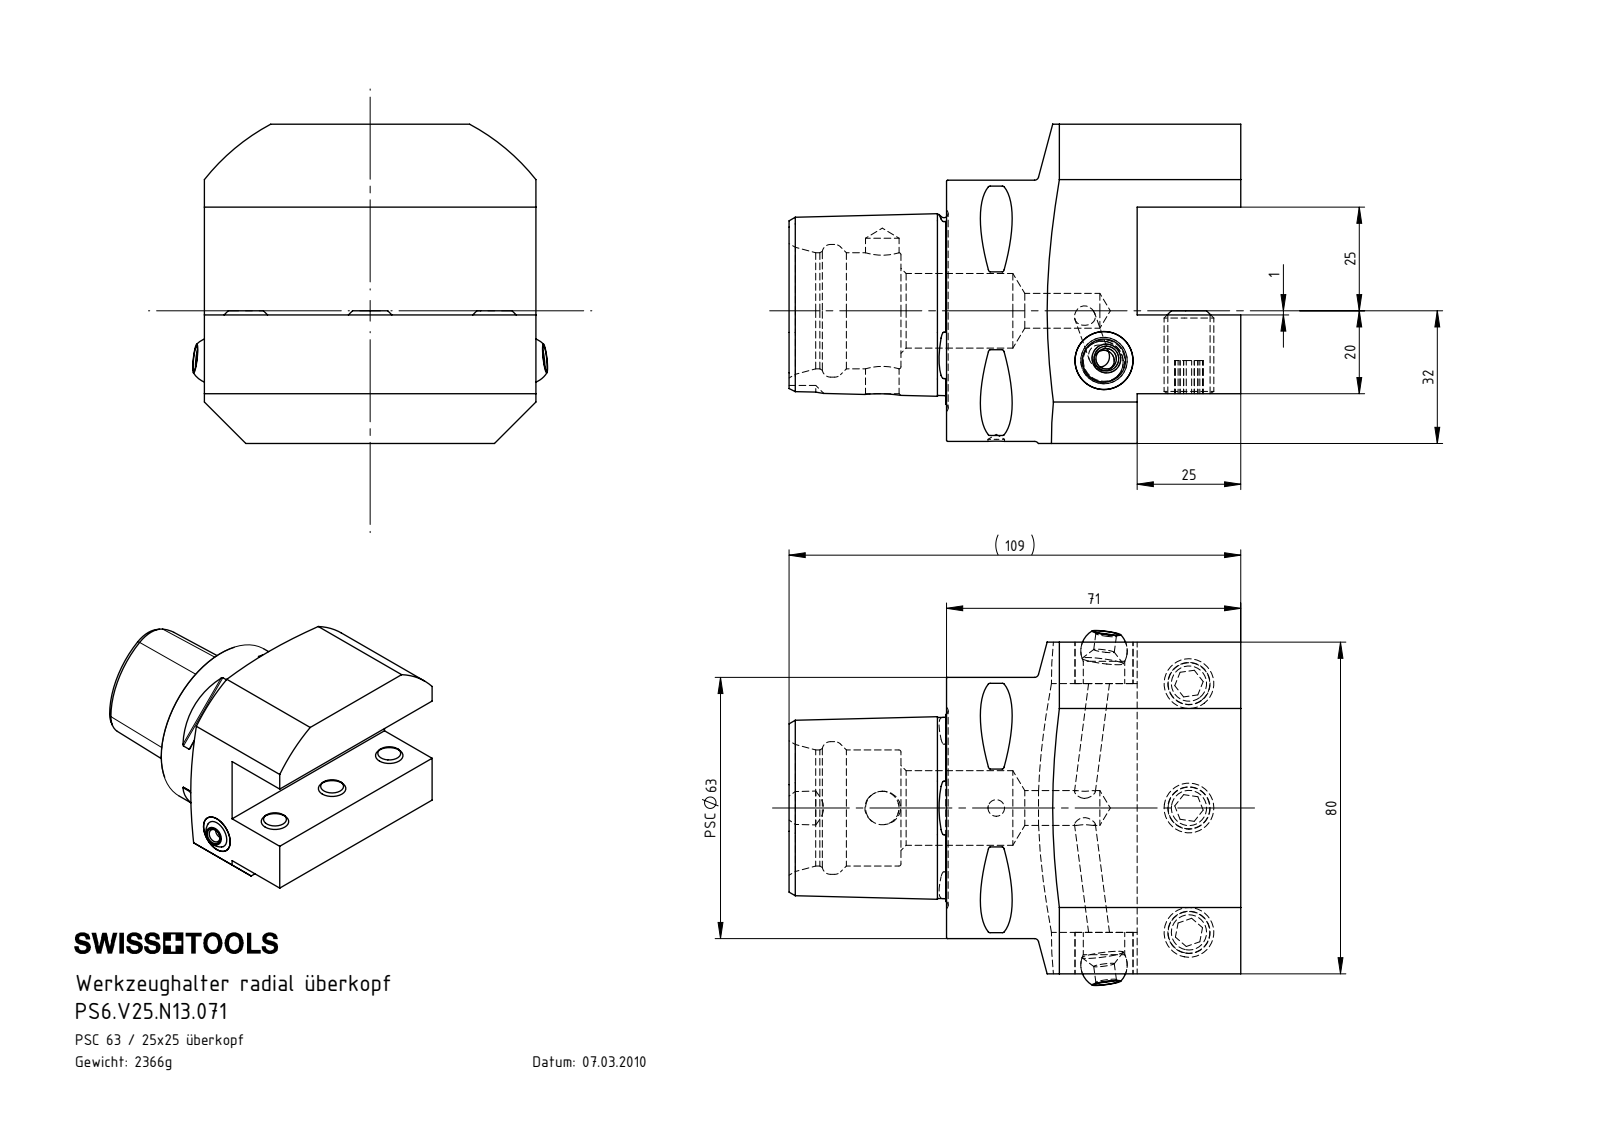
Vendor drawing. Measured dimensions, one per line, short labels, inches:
name: PS6.V25.N13.071; KU1-U14.001.012_2; PS6-V25.N13.071_A; ISO 4026 - M12 x 20 (+2 more)
written by: SolidWorks 2017 (AUTOMOTIVE_DESIGN)
unit: in
bodies: 8 solids, 167 faces (66 planar, 36 cylindrical, 65 other)
size: 4.291 × 3.371 × 3.031
volume: 18.46 in³; area: 78.23 in²
holes: 4× ⌀0.197, 3× ⌀0.402, 1× ⌀0.157, 1× ⌀0.319, 1× ⌀0.331, 1× ⌀0.394, 1× ⌀0.551, 1× ⌀0.709, 1× ⌀1.102, 1× ⌀1.26
bosses: 3× ⌀0.472, 1× ⌀2.48
rounds: 8× R0.02, 1× R0.236, 1× R2.008
face distances: 0.984, 1.811, 0.787, 1.772, 2.559, 0.748, 1.024, 2.244, 3.15, 0.472
hole spacings: 1.181, 2.179, 3.144, 1.083, 1.831, 2.362, 2.913
